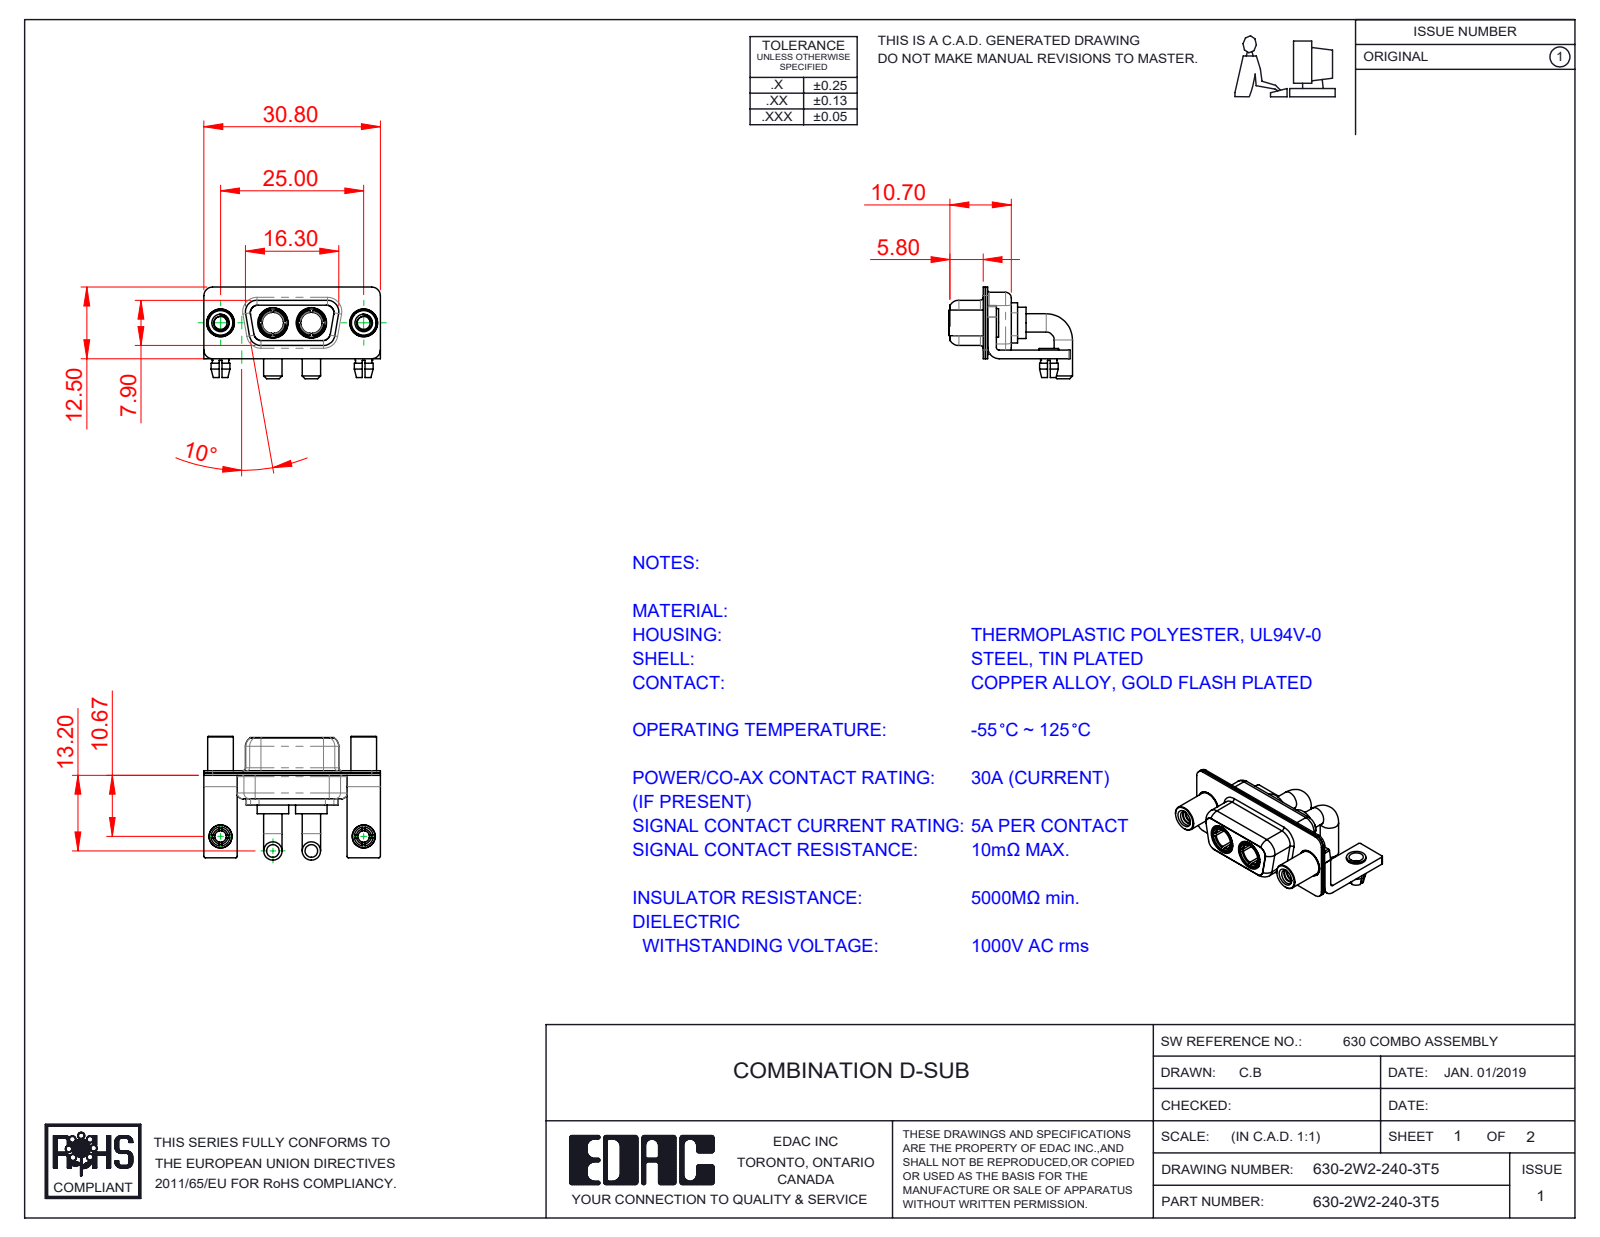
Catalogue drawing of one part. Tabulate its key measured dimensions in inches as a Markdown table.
| quantity | value |
| --- | --- |
| part name | 630Combo Housing_2W2; 630Combo Shell Front_09 Contacts; 630Combo Stabilizer Bracket; 630Combo Shell Rear_09 Contacts (+4 more) |
| STEP written by | SolidWorks 2020 (CONFIG_CONTROL_DESIGN) |
| units | inches |
| bodies | 13 solids, 615 faces (195 planar, 279 cylindrical, 141 other) |
| overall size | 1.213 × 0.85 × 0.63 |
| volume | 0.14 in³ |
| surface area | 8.61 in² |
| round holes (diameter × count) | 0.191 × 4, 0.079 × 2, 0.089 × 2, 0.098 × 2, 0.126 × 2, 0.146 × 2, 0.157 × 2, 0.159 × 2, 0.209 × 2 |
| round bosses / shafts (diameter × count) | 0.126 × 4, 0.217 × 2, 0.205 × 2, 0.197 × 2, 0.195 × 2, 0.195 × 2, 0.189 × 2, 0.187 × 2 |
| partial cylindrical surfaces (radius × count) | 0.01 × 16, 0.059 × 16, 0.079 × 13, 0.053 × 8, 0.063 × 8, 0.02 × 5, 0.024 × 4, 0.026 × 4 |
| main face-to-face distances | 0.016, 0.059, 0.031, 0.055, 0.018, 0.333, 0.071, 0.091, 0.35, 0.146 |
| hole center spacings | 0.36, 0.624, 0.984, 0.265 |
